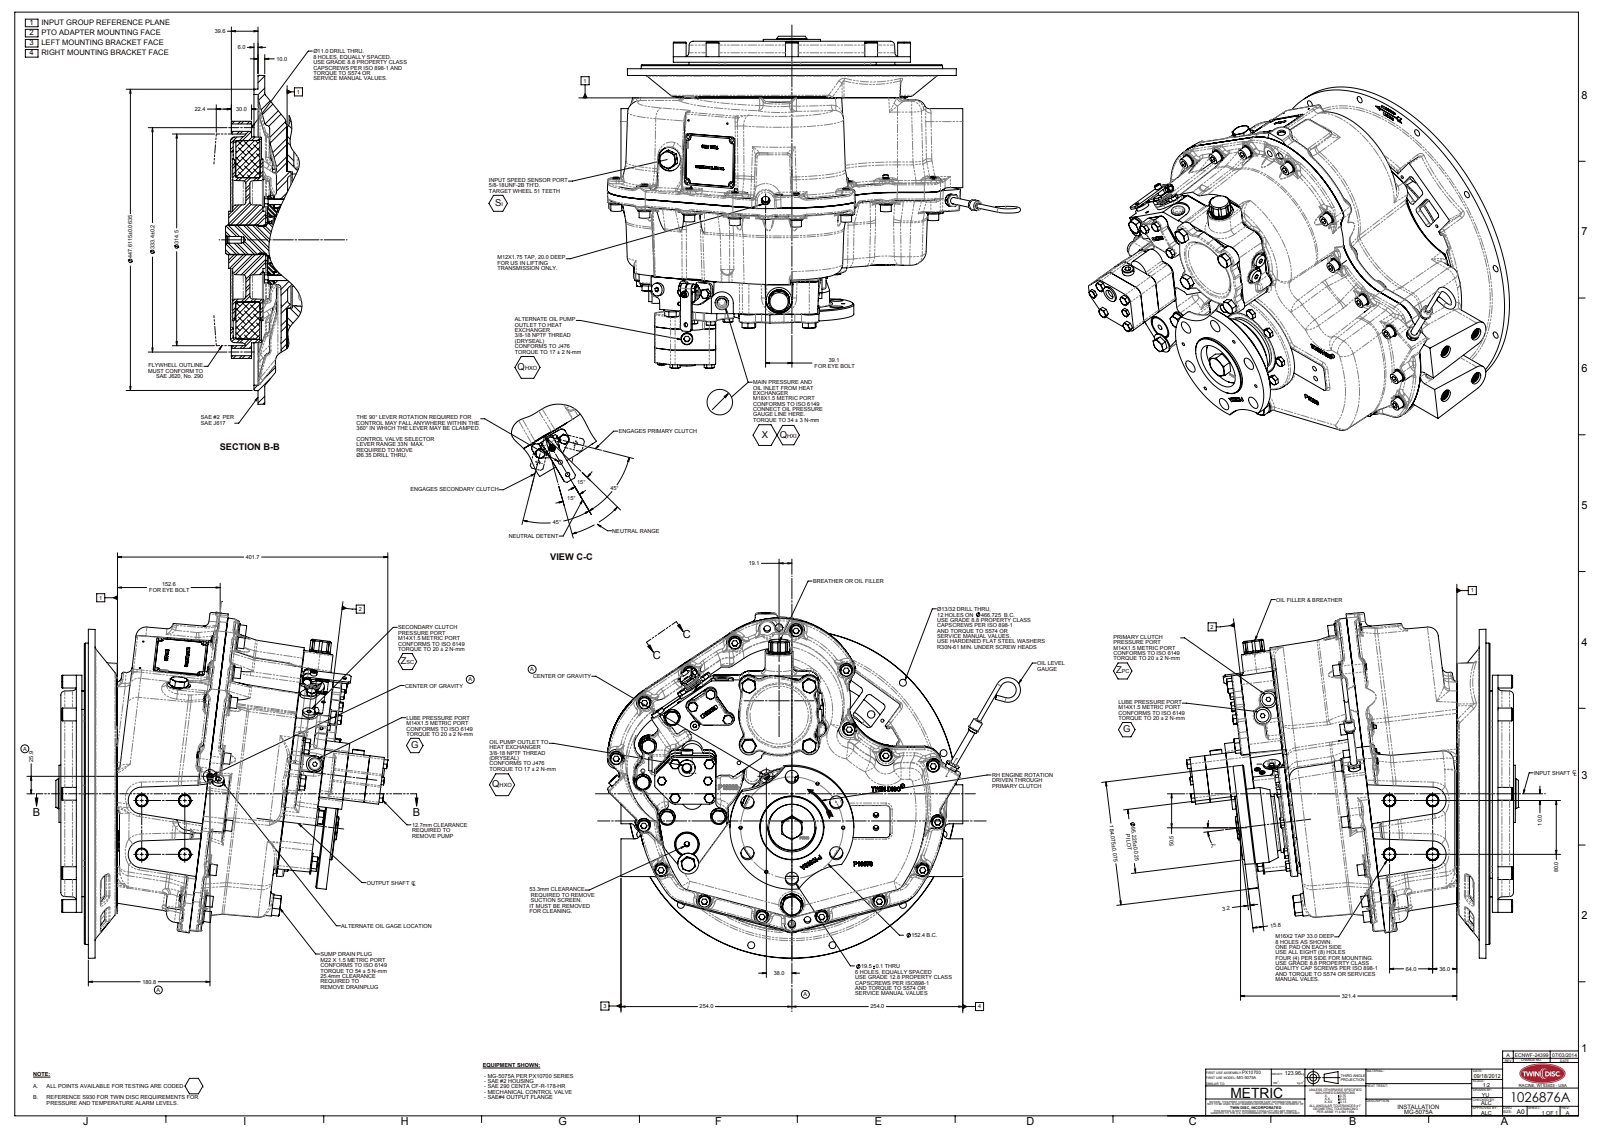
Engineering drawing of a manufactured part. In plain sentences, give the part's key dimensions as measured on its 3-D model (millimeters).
The part is named "1026876A". Its 3-D file was written by "SolidWorks 2010 (AUTOMOTIVE_DESIGN)". It is 0 solids with 8269 faces: 3828 planar, 1966 cylindrical and 2475 other. Overall it measures 613.93 by 513.92 by 493.27 millimeters. Round holes: 12 of diameter 10.32, 8 of diameter 11, 6 of diameter 19.5, 4 of diameter 5, 4 of diameter 18.82, 3 of diameter 8, 3 of diameter 10, 3 of diameter 95.24, 2 of diameter 2.5, 2 of diameter 4.6, 2 of diameter 5.3, 2 of diameter 6.35. Round bosses or shafts: 17 of diameter 19.85, 17 of diameter 16, 12 of diameter 19, 12 of diameter 15.88, 11 of diameter 10, 5 of diameter 24, 3 of diameter 6.35, 2 of diameter 125.7. Partial cylindrical surfaces (rounded edges, fillets, slot ends): 284 of radius 16.96, 169 of radius 0.8, 154 of radius 1.27, 104 of radius 2, 73 of radius 5, 54 of radius 4, 38 of radius 2.5, 30 of radius 8. The main face-to-face distances are 0.42, 8.5, 8.92, 0.39, 0.45, 52.45, 117.92, 117.95, 118.34, 118.37. The hole center spacings are 76.2, 127.58, 165.03, 233.37, 286.79, 308.02, 370.5, 147.21.
